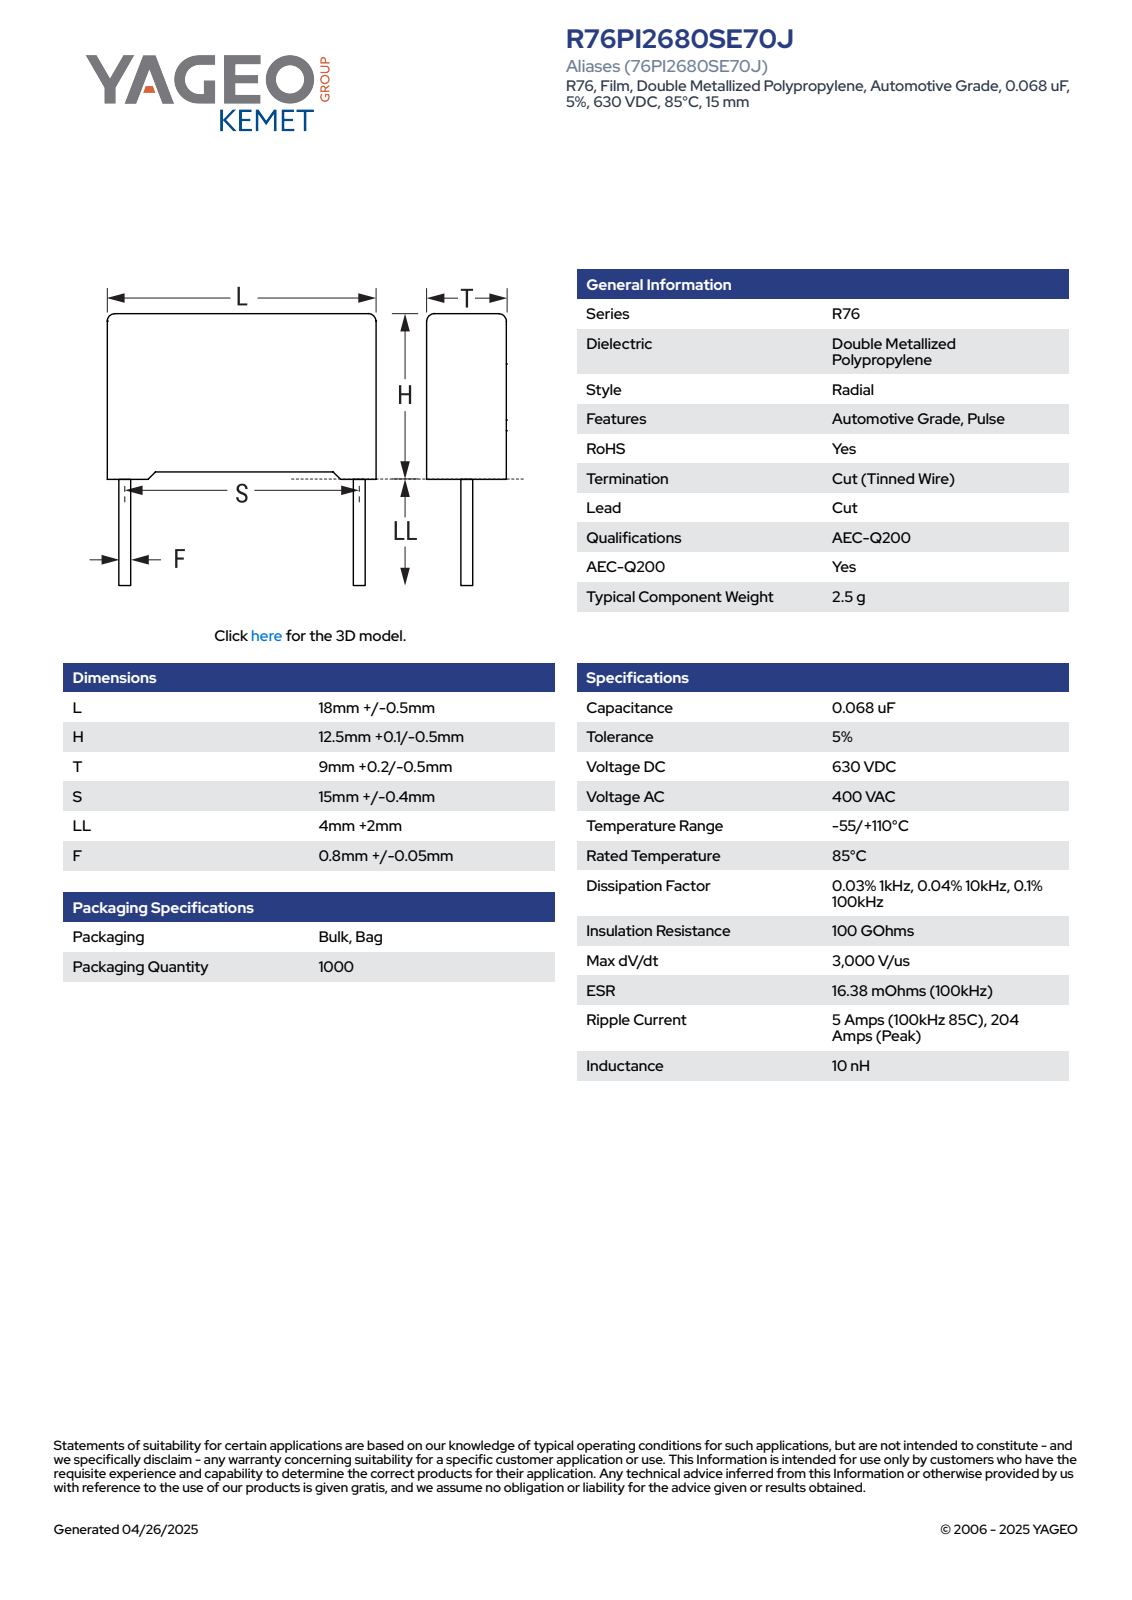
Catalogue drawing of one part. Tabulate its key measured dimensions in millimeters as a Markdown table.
| quantity | value |
| --- | --- |
| part name | CFR_RB2_18X12.5X9_L18.5H12.6T9.2S15LL6F0.85 |
| STEP written by | SolidWorks 2021 (AUTOMOTIVE_DESIGN) |
| units | millimeters |
| bodies | 4 solids, 85 faces (77 planar, 8 cylindrical, 0 other) |
| overall size | 18.6 × 18.5 × 9.21 |
| volume | 2 040 mm³ |
| surface area | 1 107 mm² |
| round bosses / shafts (diameter × count) | 0.85 × 2 |
| partial cylindrical surfaces (radius × count) | 0.5 × 4 |
| main face-to-face distances | 9.2, 11.85, 18.5, 0.62, 0.75, 12.6, 8.58, 0.43, 0.32, 12.17 |
